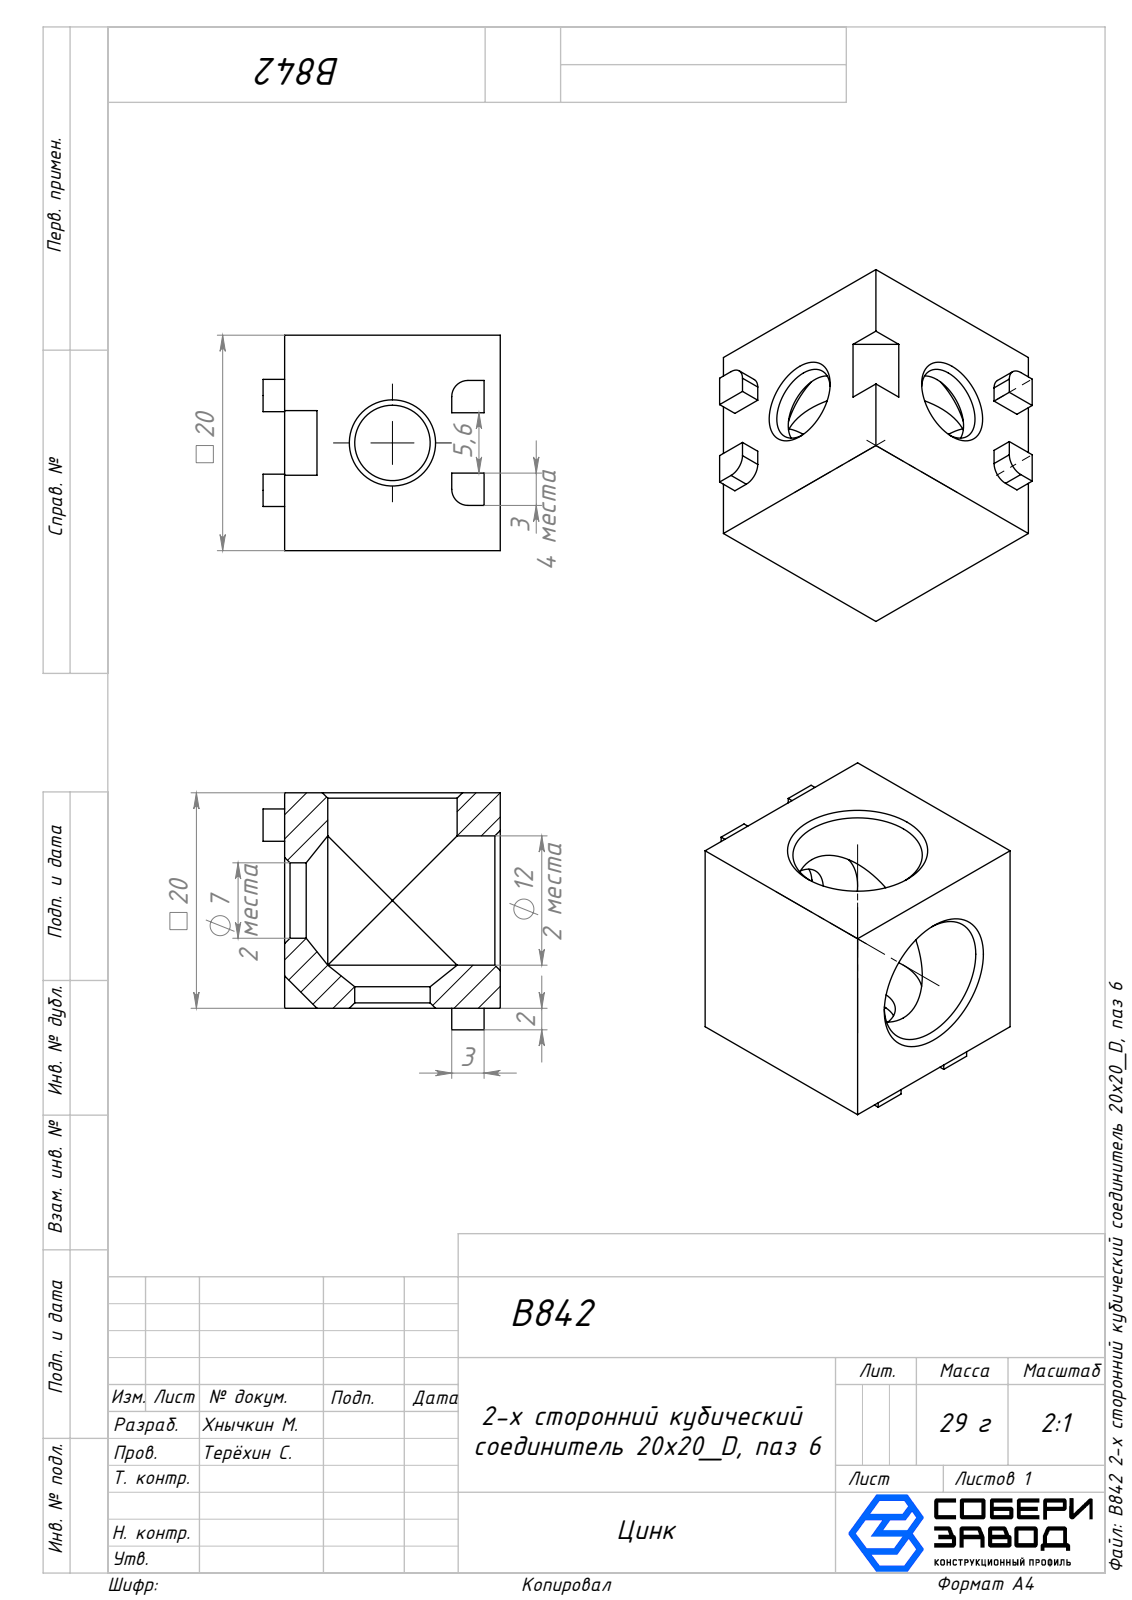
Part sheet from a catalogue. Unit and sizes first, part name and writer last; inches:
Units: inches
Overall size (bounding box): 0.866 × 0.866 × 0.787
Round holes (diameter × count): ⌀0.276 ×2, ⌀0.472 ×2
Partial cylindrical surfaces — rounded edges, fillets, slot ends (radius × count): R0.059 ×4
Main face-to-face distances: 0.787, 0.079, 0.866, 0.118, 0.807, 0.728, 0.059, 0.228, 0.114, 0.343
Volume: 0.312 in³ · Surface area: 4.746 in²
Bodies: 1 solid, 59 faces (29 planar, 18 cylindrical, 12 other)
Part name (STEP PRODUCT): B842 2-х сторонний кубический соединитель 20х20_D, паз 6
STEP written by: SolidWorks 2025 (AUTOMOTIVE_DESIGN)
